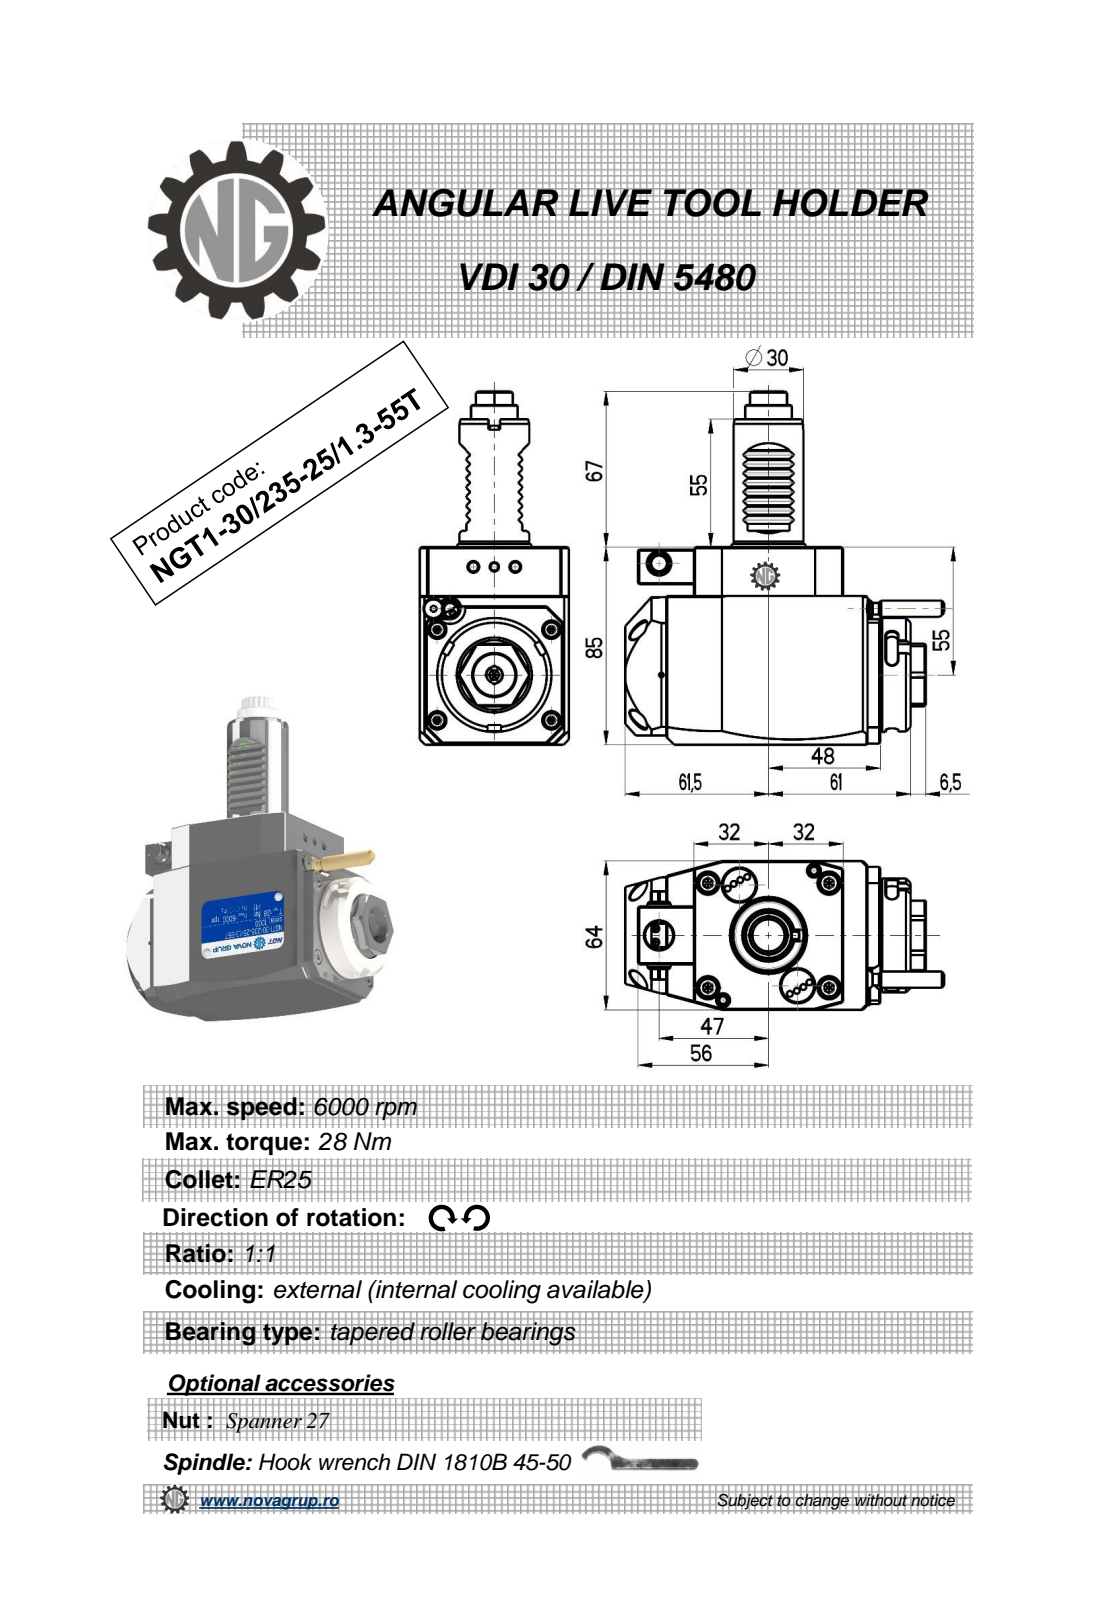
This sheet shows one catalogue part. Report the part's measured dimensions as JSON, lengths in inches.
{"part_name": "NGT1_30_235_25_1_3_55T", "step_written_by": "PRO/ENGINEER BY PARAMETRIC TECHNOLOGY CORPORATION, 2010280 (CONFIG_CONTROL_DESIGN)", "units": "inches", "bodies": {"solids": 1, "faces": 466, "planar": 215, "cylindrical": 161, "other": 90}, "overall_size": [5.984, 5.389, 2.52], "volume_in3": 34, "surface_area_in2": 79.44, "round_holes": [[0.098, 1], [0.118, 1], [0.374, 1], [0.472, 1], [0.709, 1]], "round_bosses_or_shafts": [[0.315, 2], [1.929, 1], [1.654, 1], [1.181, 1], [0.787, 1], [0.394, 1], [0.276, 1], [0.197, 1]], "partial_cylinders_radius": [[0.078, 36], [0.012, 16], [0.098, 6], [7.087, 2], [0.152, 1], [0.167, 1], [0.177, 1], [0.279, 1]], "face_to_face_distances": [2.52, 3.346, 0.63, 0.512, 4.311, 0.827, 3.15, 4.823, 1.142, 3.681], "hole_center_spacings": [1.03, 1.348, 1.831]}
